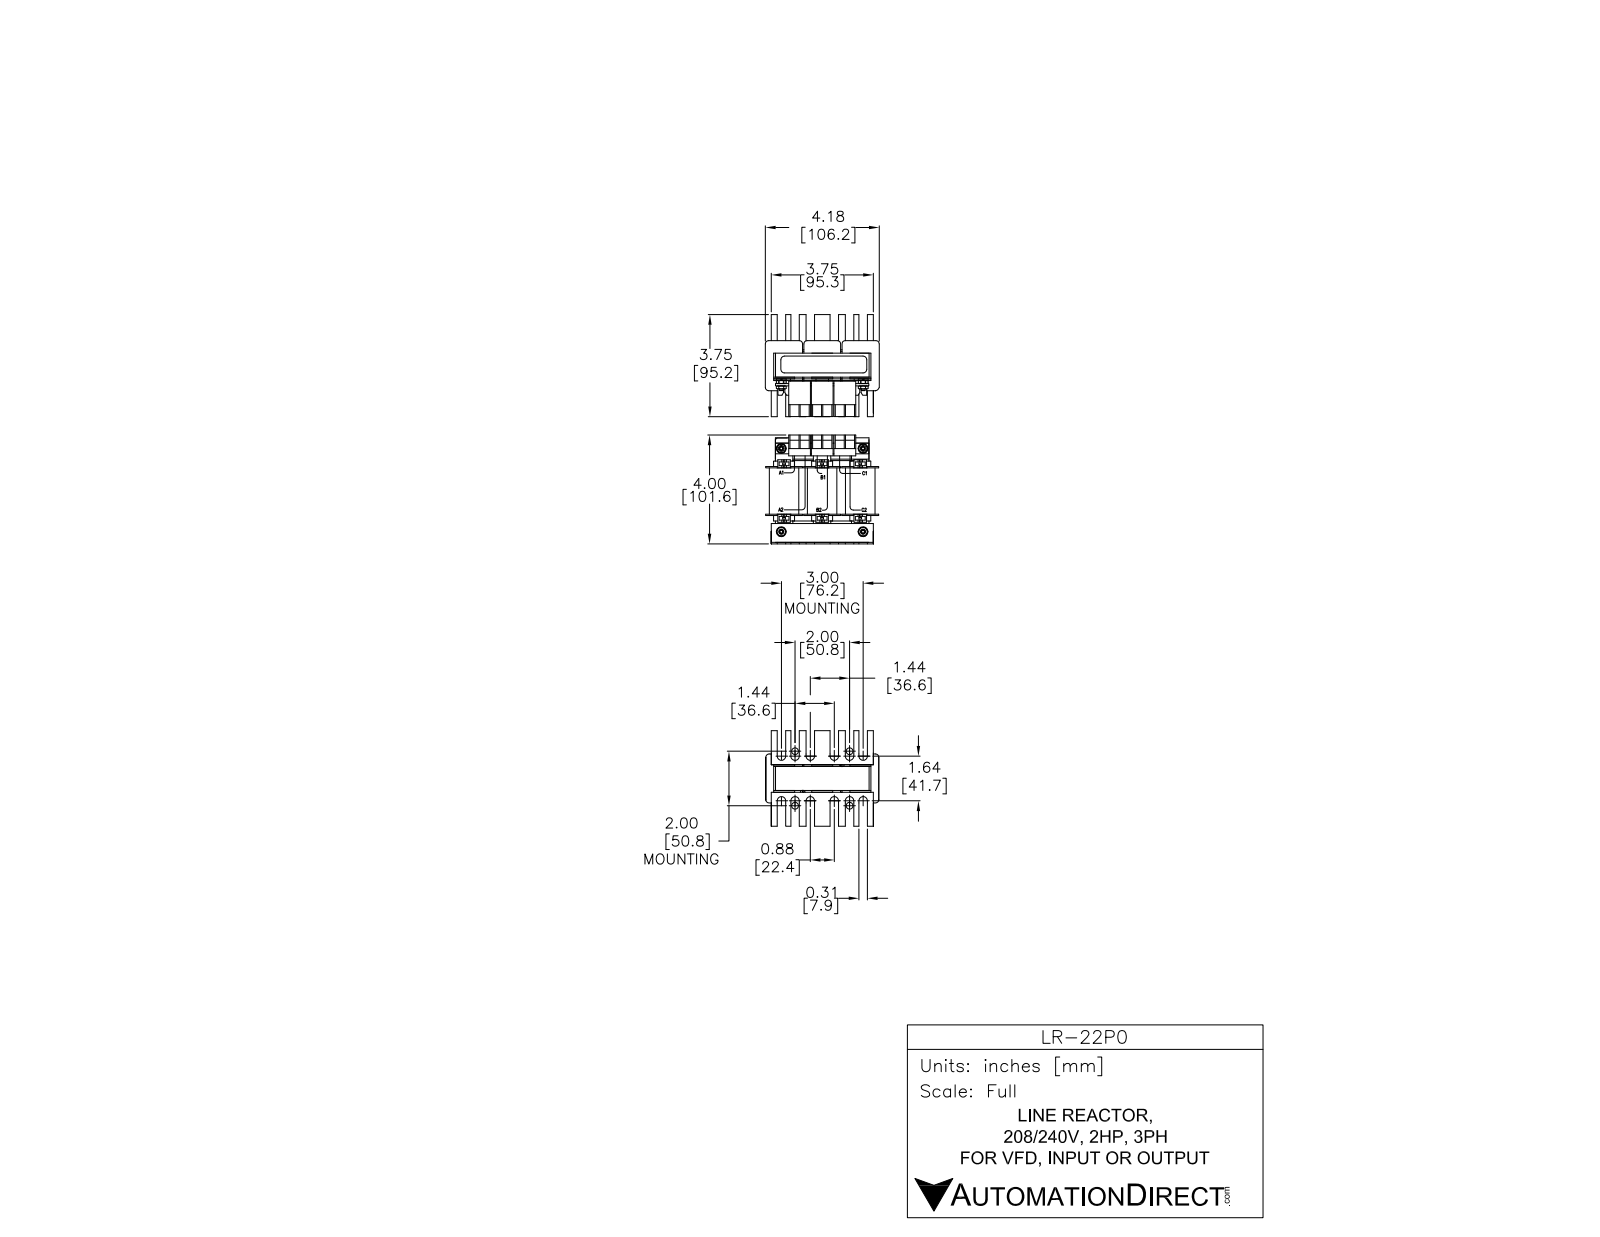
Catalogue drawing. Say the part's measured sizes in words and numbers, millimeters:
The part is named "LR-22P0". Its 3-D file was written by "SolidWorks 2011 (AUTOMOTIVE_DESIGN)". It is 17 solids with 941 faces: 743 planar, 198 cylindrical and 0 other. Overall it measures 105.25 by 98.41 by 89.25 millimeters. Its volume is 272 326 cubic millimeters and its surface area 99 223 square millimeters. Round bosses or shafts: 4 of diameter 7.75, 4 of diameter 3.5. Partial cylindrical surfaces (rounded edges, fillets, slot ends): 50 of radius 4, 24 of radius 1.82, 12 of radius 8, 6 of radius 3, 3 of radius 0.86, 2 of radius 1.25. The main face-to-face distances are 5, 21.5, 2.75, 51, 26.25, 26.5, 7.5, 29, 71, 2.5.
